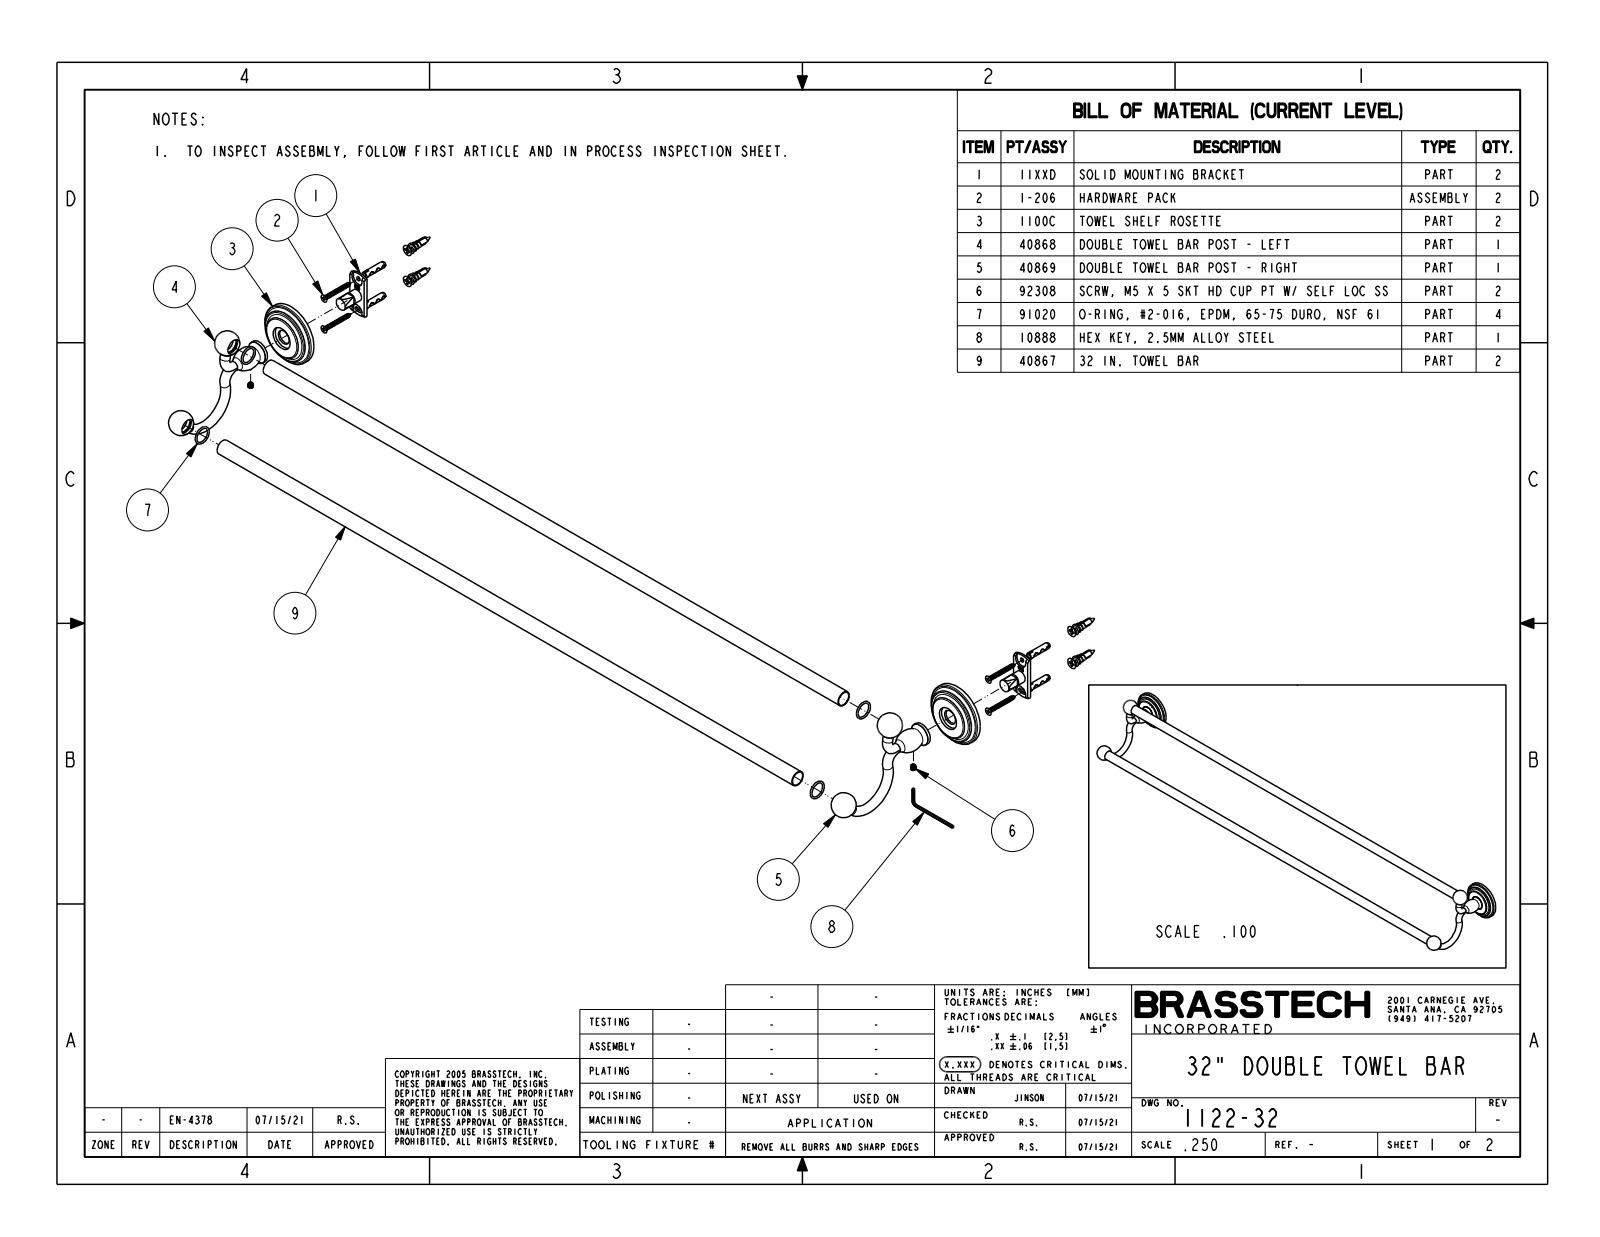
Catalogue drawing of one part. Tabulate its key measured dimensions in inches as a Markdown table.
| quantity | value |
| --- | --- |
| part name | 1122-32 |
| STEP written by | CREO PARAMETRIC BY PTC INC, 2018400 (CONFIG_CONTROL_DESIGN) |
| units | inches |
| bodies | 1 solid, 104 faces (12 planar, 32 cylindrical, 60 other) |
| overall size | 34.56 × 5.218 × 4.054 |
| volume | 27.41 in³ |
| surface area | 177.1 in² |
| round holes (diameter × count) | 0.65 × 2 |
| round bosses / shafts (diameter × count) | 0.394 × 4, 2.56 × 2, 2.182 × 2, 1.748 × 2, 0.625 × 2 |
| main face-to-face distances | 0.512, 0.362, 0.15, 0.189, 0.173, 0.323, 31.362 |
| hole center spacings | 3.62 |
